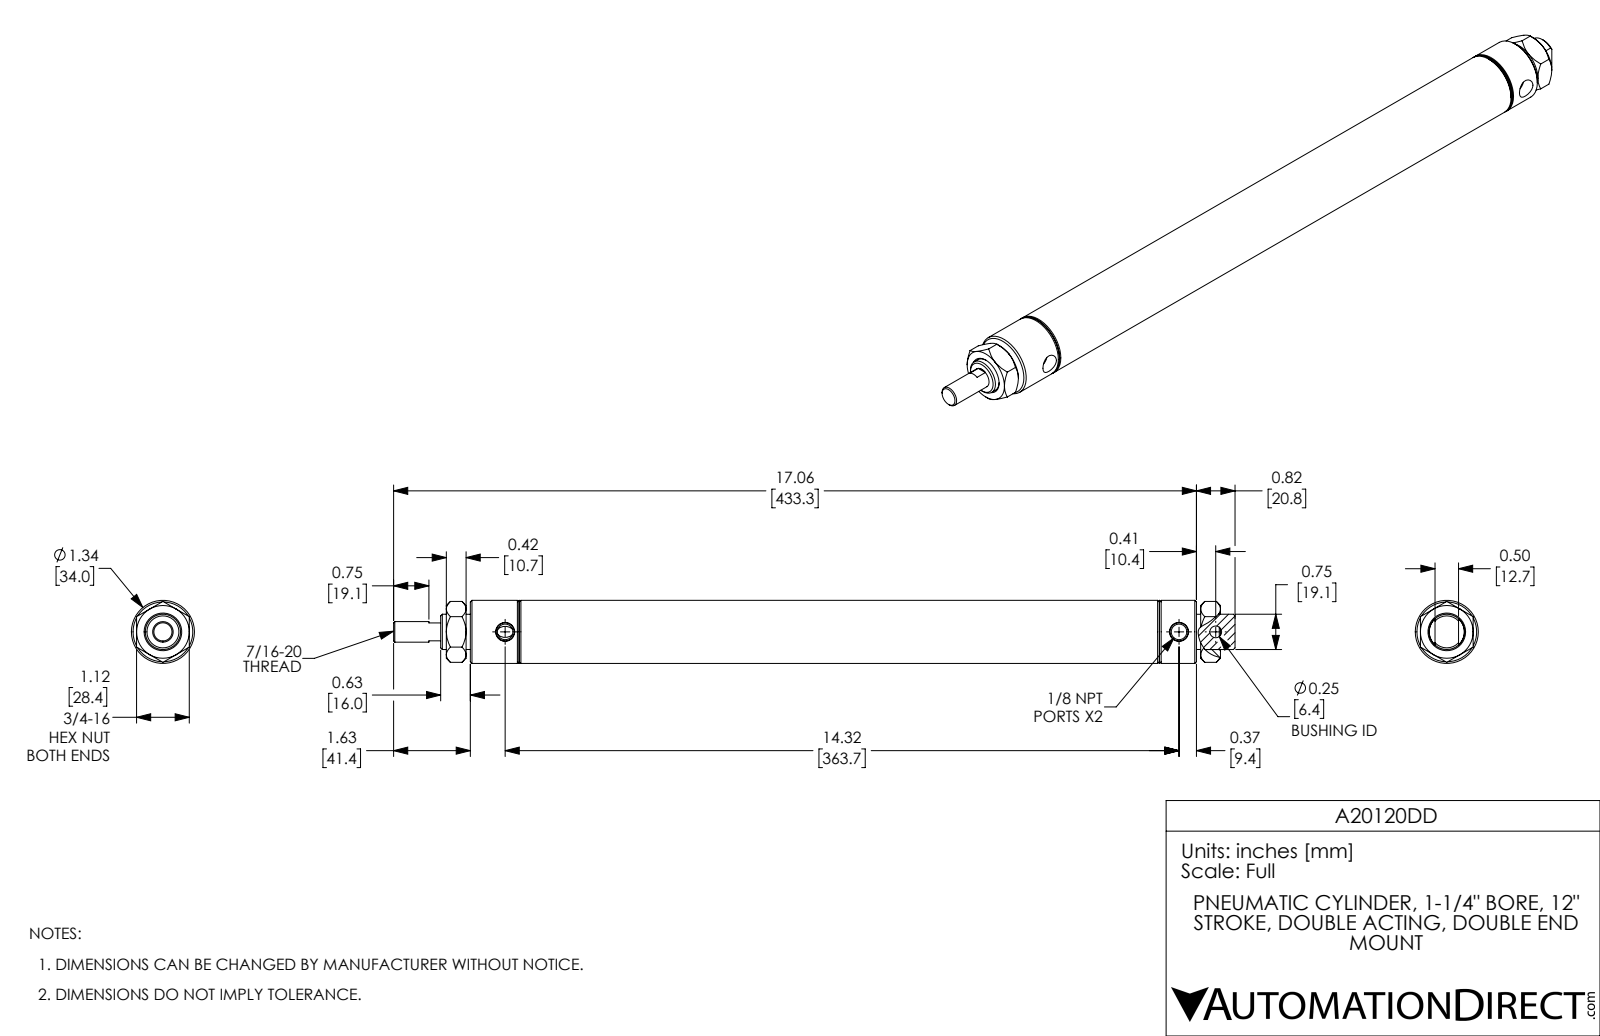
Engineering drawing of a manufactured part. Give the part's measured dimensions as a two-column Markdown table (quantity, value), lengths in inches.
| quantity | value |
| --- | --- |
| part name | A20120DD; A20120DD_Mounting Nut_D-3556; A20120DD-Rod; A20120DD-MainBody |
| STEP written by | SolidWorks 2017 (AUTOMOTIVE_DESIGN) |
| units | inches |
| bodies | 4 solids, 138 faces (44 planar, 36 cylindrical, 58 other) |
| overall size | 17.88 × 1.34 × 1.34 |
| volume | 9.936 in³ |
| surface area | 159.5 in² |
| round holes (diameter × count) | 0.332 × 2, 0.251 × 1, 0.437 × 1, 0.75 × 1, 1.25 × 1 |
| round bosses / shafts (diameter × count) | 1.34 × 1, 0.747 × 1 |
| main face-to-face distances | 1.465, 13.965, 0.5, 1.12, 12.5, 12, 0.31, 0.42, 16.03, 1.965 |
| hole center spacings | 0.78, 14.32, 15.1 |
